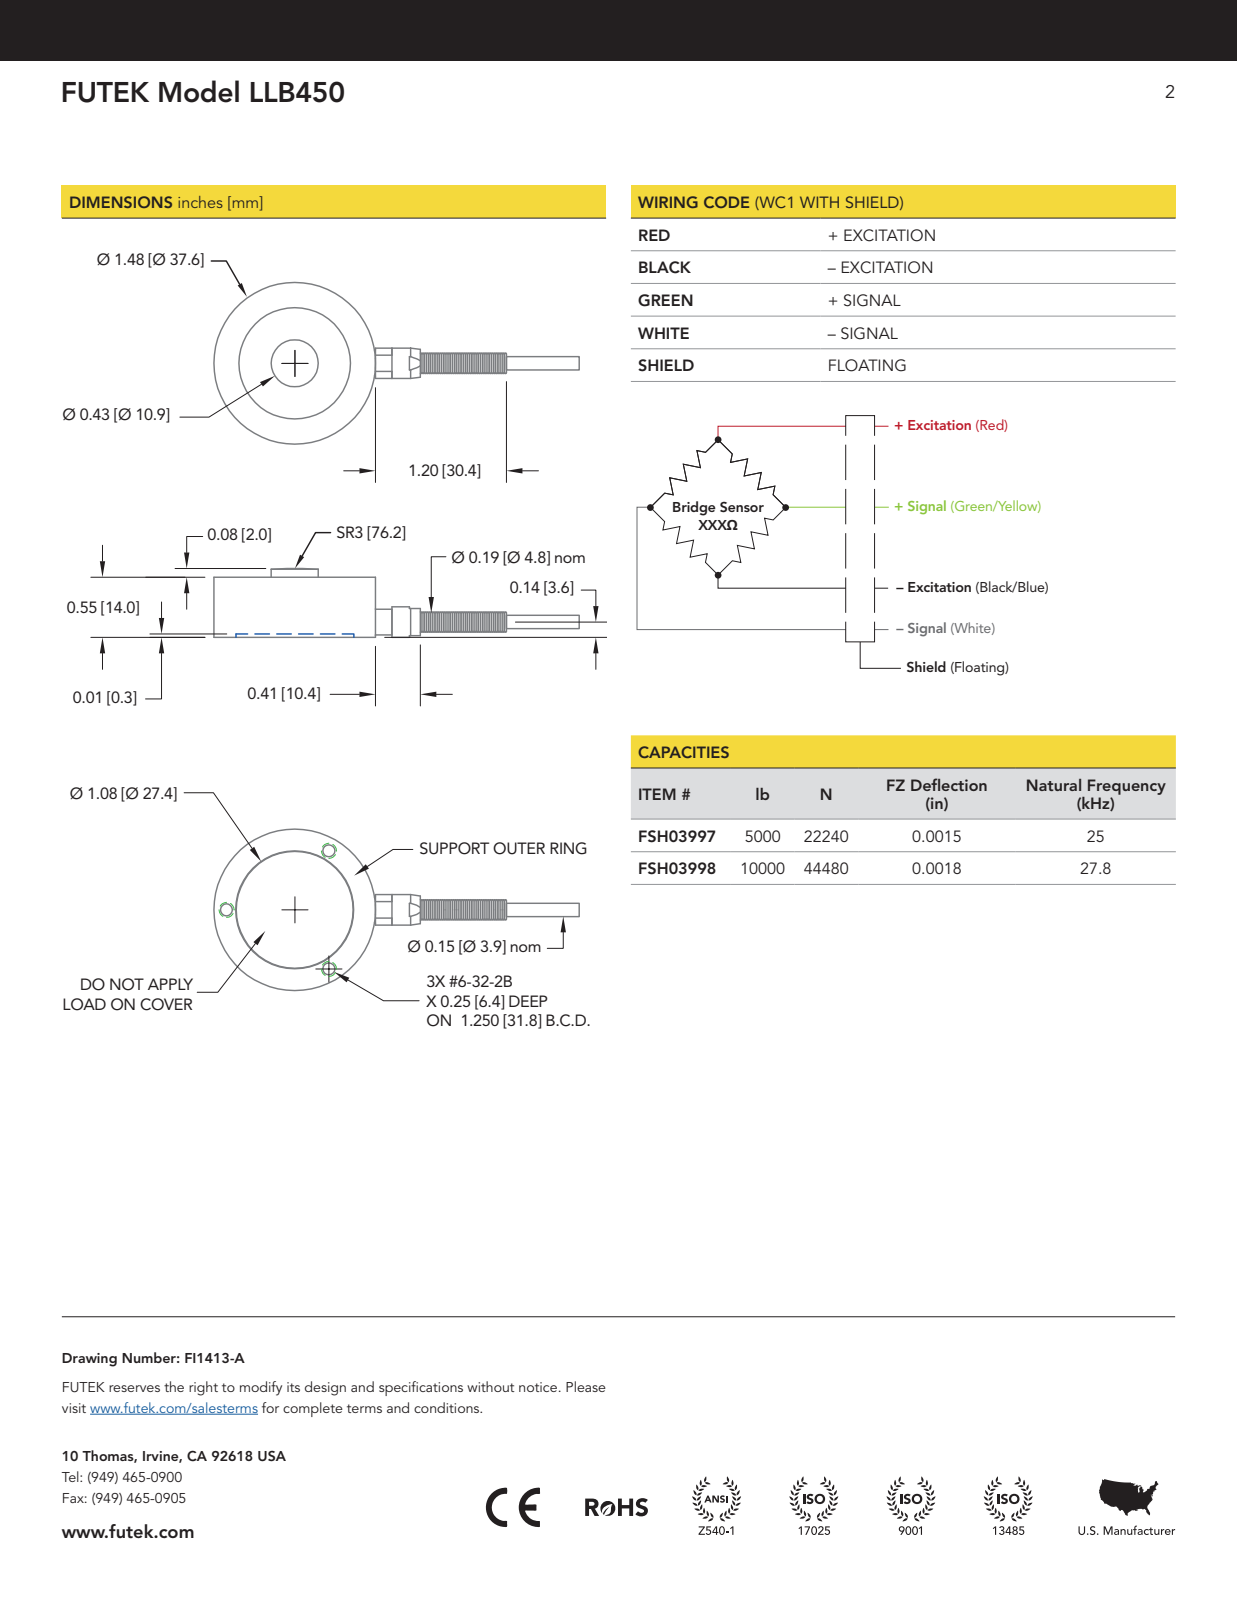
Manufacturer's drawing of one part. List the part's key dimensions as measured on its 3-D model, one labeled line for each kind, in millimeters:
Part name (STEP PRODUCT): LLB450 (LevelofDetail1); ~~~PART1; 4925; 4925A (+1 more)
STEP written by: Autodesk Inventor 2008 (AUTOMOTIVE_DESIGN)
Units: millimetres
Bodies: 3 solids, 120 faces (24 planar, 18 cylindrical, 78 other)
Overall size (bounding box): 130 × 37.6 × 16.2
Volume: 15 900 mm³ · Surface area: 6 372 mm²
Round holes (diameter × count): ⌀2.8 ×3, ⌀3.3 ×1, ⌀3.9 ×1, ⌀4.8 ×1, ⌀5.3 ×1, ⌀5.6 ×1, ⌀5.8 ×1, ⌀25.9 ×1, ⌀27.4 ×1
Round bosses / shafts (diameter × count): ⌀3.2 ×3, ⌀37.6 ×1, ⌀26.7 ×1, ⌀10.9 ×1, ⌀7.1 ×1
Main face-to-face distances: 13.7, 14, 0.5, 13.2, 13.5, 0.8, 12.7, 6.5, 6.3, 5.8
Hole centre spacings: 27.5, 15.9, 15.9
